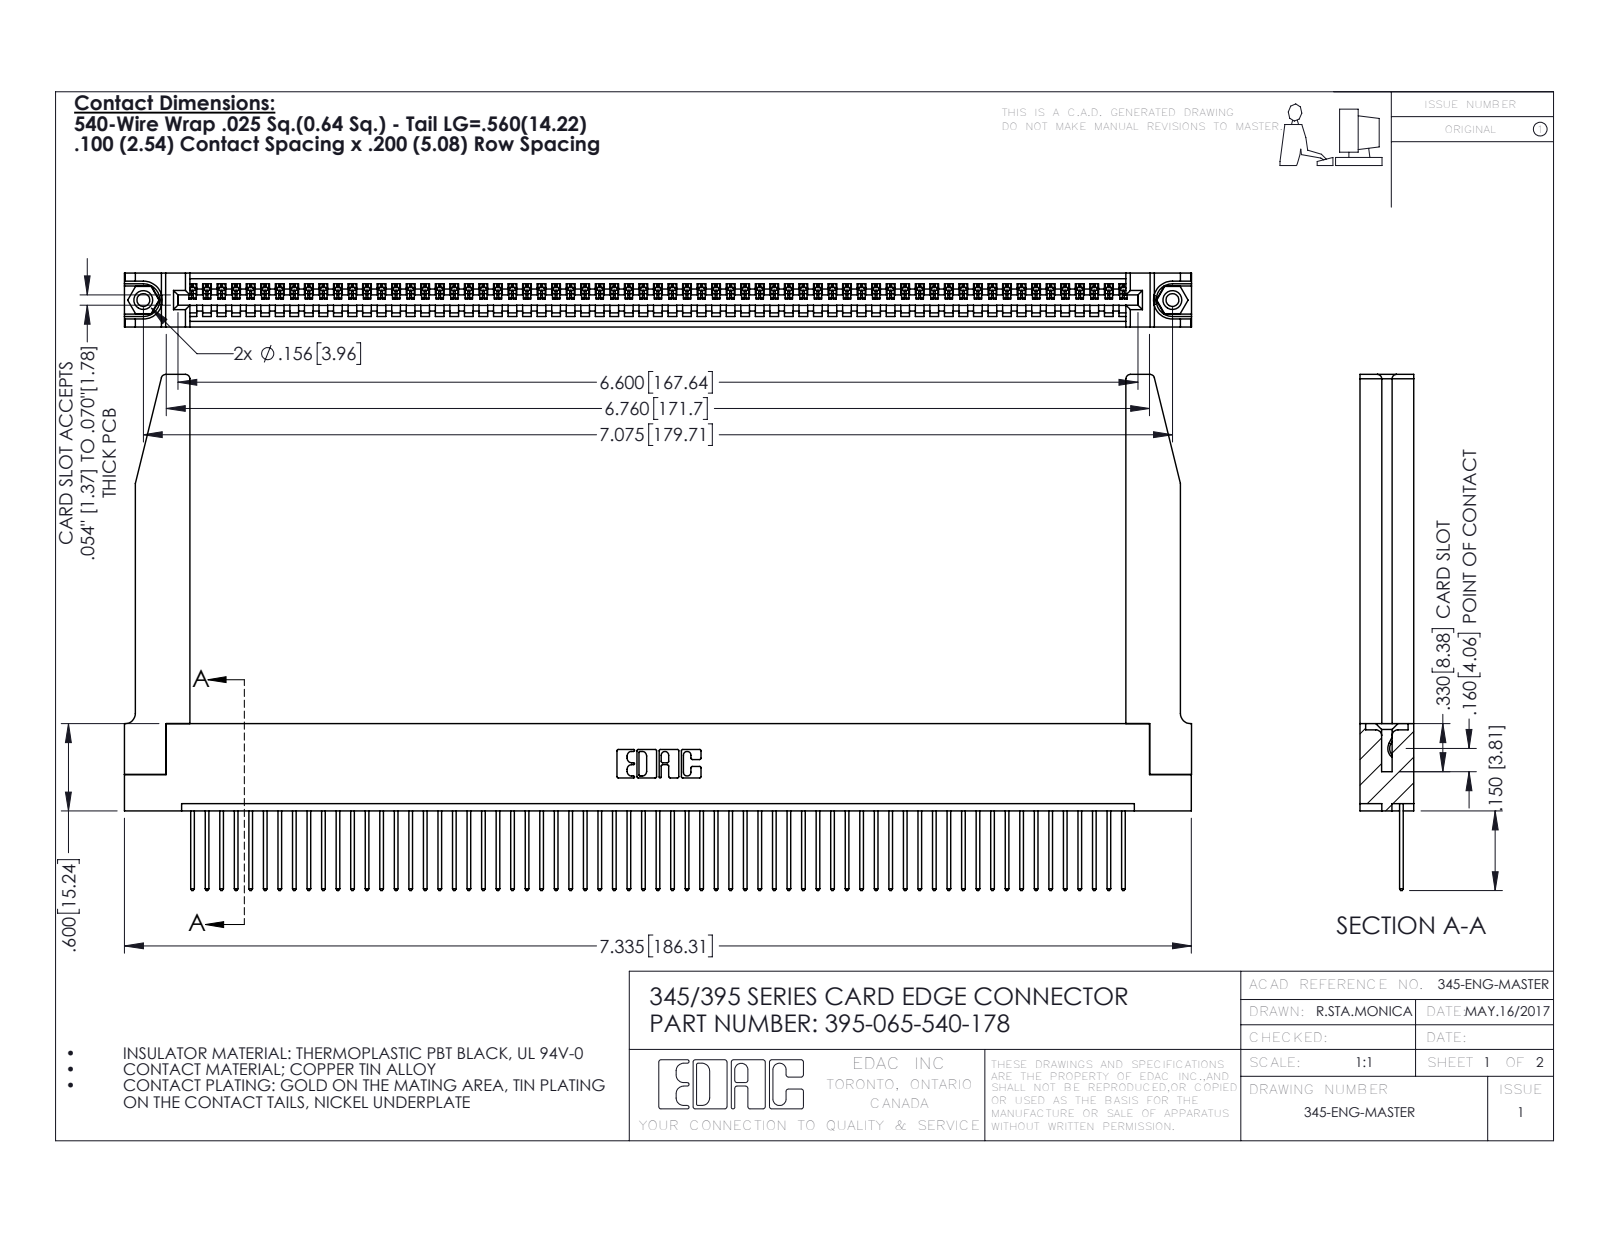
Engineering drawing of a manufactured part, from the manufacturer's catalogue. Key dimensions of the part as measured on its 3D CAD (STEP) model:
Part name (STEP PRODUCT): 345-220-078_345-220-078; 345 Part_Flush Mounting Lugs - 0.156 Dia-TH; 345-250-001_345-250-001-102; 395-065-540-178 (+1 more)
STEP written by: SolidWorks 2016 (CONFIG_CONTROL_DESIGN)
Units: inches
Bodies: 70 solids, 4130 faces (2822 planar, 1256 cylindrical, 52 other)
Overall size (bounding box): 7.336 × 3.547 × 0.37
Volume: 1.571 in³ · Surface area: 49.1 in²
Round holes (diameter × count): ⌀0.089 ×2, ⌀0.125 ×2, ⌀0.156 ×2, ⌀0.064 ×1
Round bosses / shafts (diameter × count): ⌀0.155 ×2
Partial cylindrical surfaces — rounded edges, fillets, slot ends (radius × count): R0.006 ×130, R0.01 ×130, R0.01 ×22, R0.03 ×8, R0.007 ×6, R0.031 ×6, R0.026 ×3, R0.031 ×2
Main face-to-face distances: 0.072, 0.298, 0.37, 0.098, 0.272, 0.025, 0.2, 0.225, 0.148, 0.15
Hole centre spacings: 0.27, 6.839, 7.075
